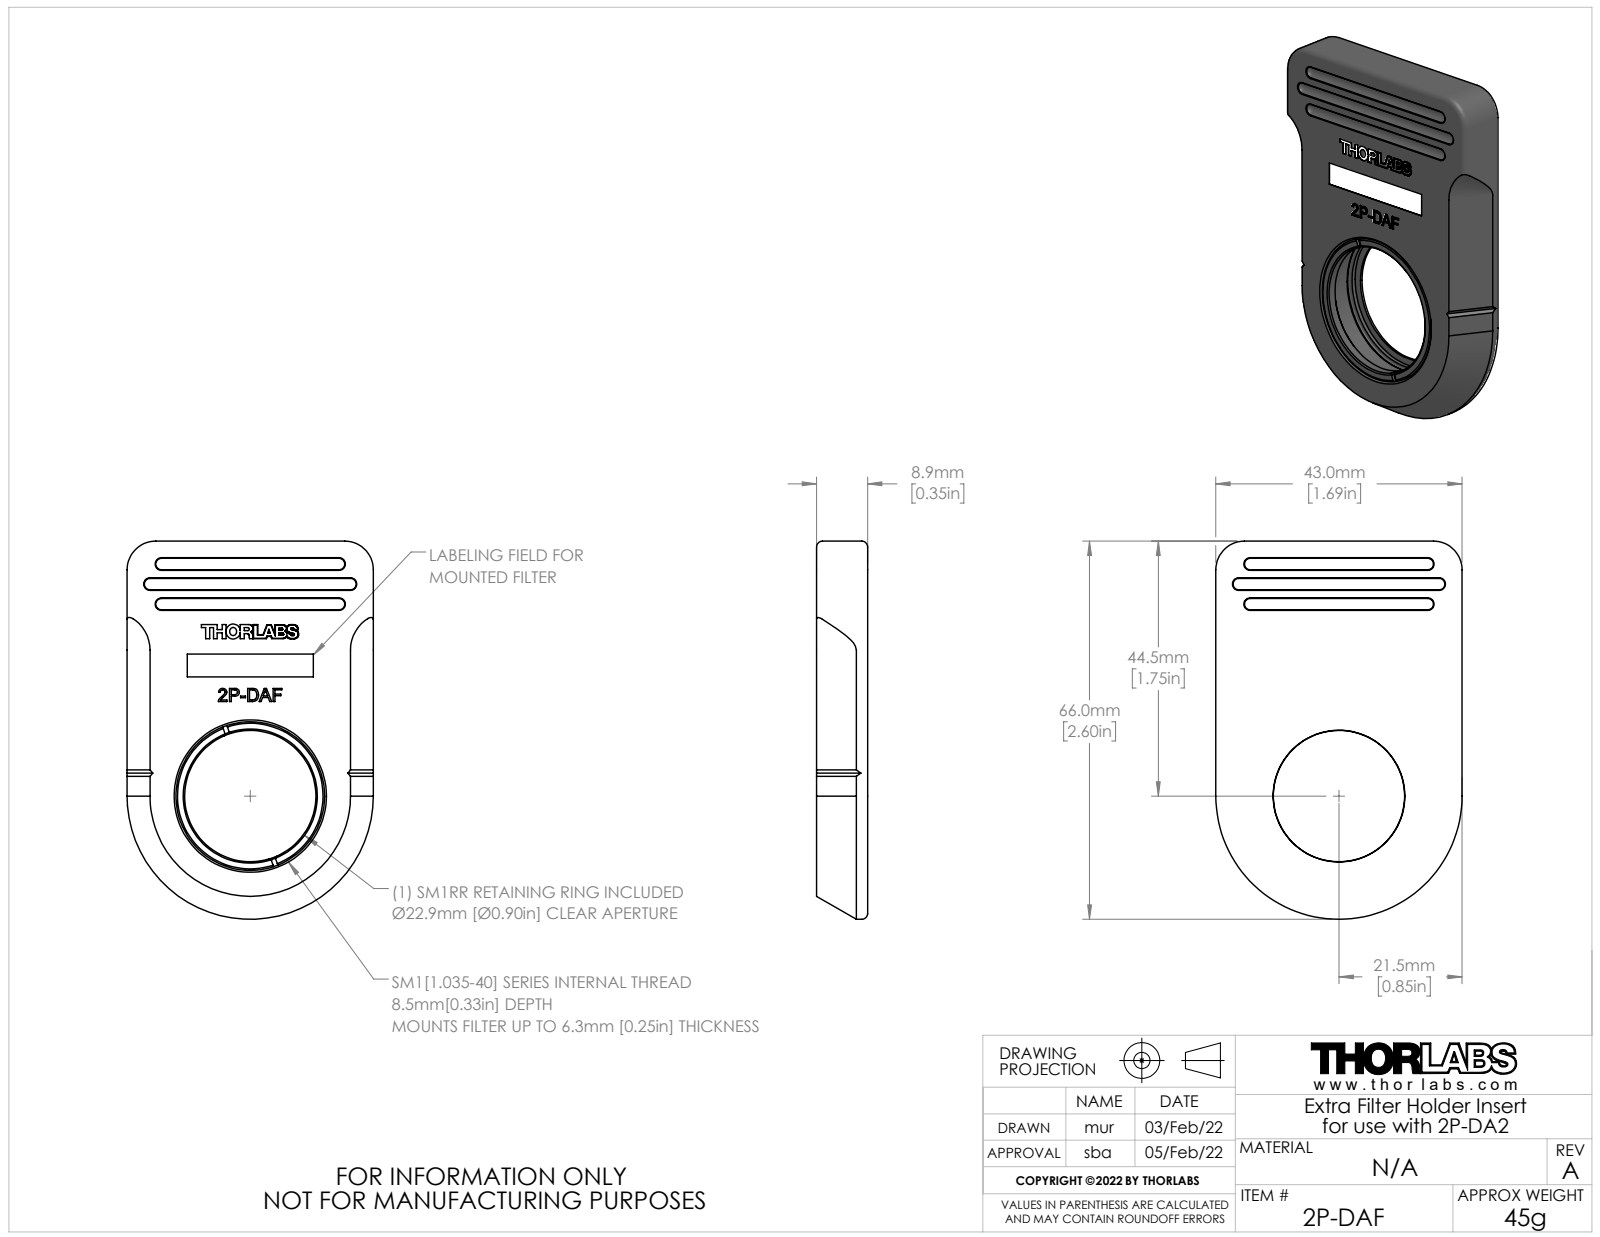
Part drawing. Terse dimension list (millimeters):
name: 22.03.04_2P-DAF_Filter Holder Insert WEB
written by: SolidWorks 2019 (AUTOMOTIVE_DESIGN)
unit: mm
bodies: 2 solids, 572 faces (472 planar, 27 cylindrical, 73 other)
size: 66 × 43 × 8.9
volume: 16 923 mm³; area: 7 140 mm²
holes: 1× ⌀22.91, 1× ⌀23, 1× ⌀25.5, 1× ⌀25.96, 1× ⌀26.5
bosses: 1× ⌀26.29
rounds: 12× R1, 2× R5, 1× R21.5
face distances: 8.9, 8.89, 43, 8.5, 8.49, 0.4, 2.19, 2.2, 6.3, 6.7
